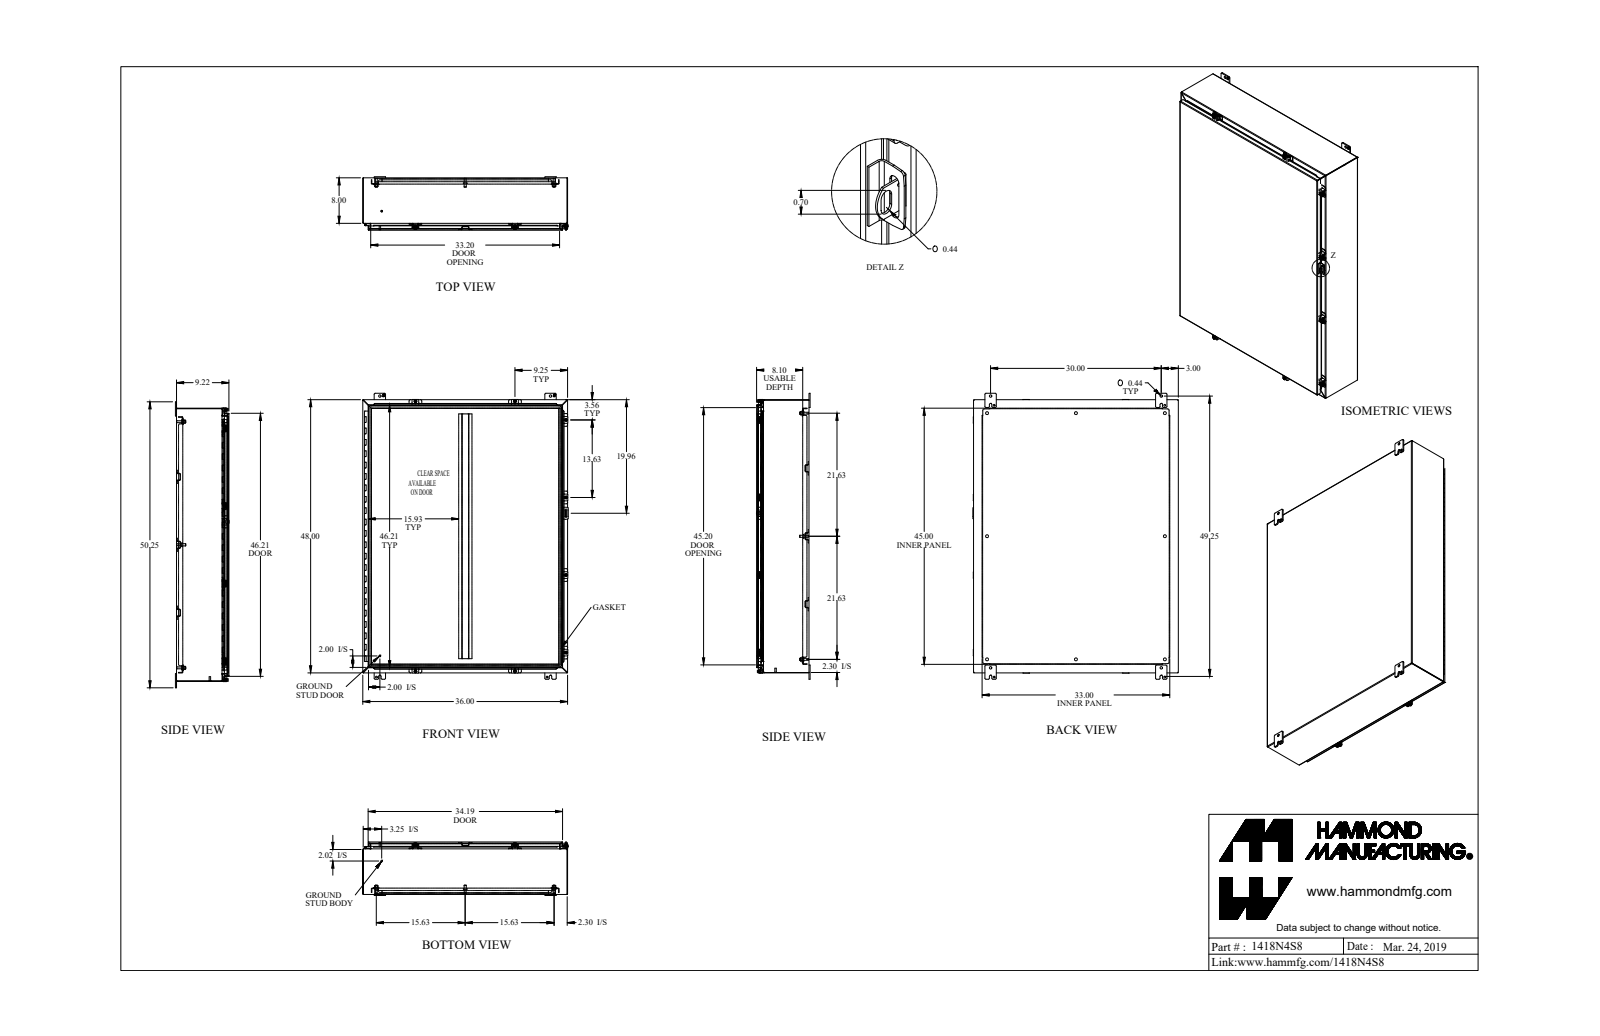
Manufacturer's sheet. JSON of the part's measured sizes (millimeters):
{"part_name": "1418N4S8_Default", "step_written_by": "SolidWorks 2019 (CONFIG_CONTROL_DESIGN)", "units": "millimeters", "bodies": {"solids": 67, "faces": 2413, "planar": 1405, "cylindrical": 876, "other": 132}, "overall_size": [1276.4, 917.6, 239.7], "volume_mm3": 9563000, "surface_area_mm2": 9792000, "round_holes": [[5.4, 8], [6.7, 8], [9.5, 8], [12.7, 8], [7.8, 4], [8, 4], [11.1, 4], [11.3, 4], [3.2, 1], [4.7, 1]], "round_bosses_or_shafts": [[16.5, 8], [12.7, 8], [9.9, 8], [9.5, 8], [8.4, 8], [6.2, 8], [25.4, 4], [7.1, 2]], "partial_cylinders_radius": [[6.4, 48], [1.2, 39], [3.6, 39], [4.8, 37], [0.9, 24], [2.7, 24], [2.9, 16], [3.6, 16]], "face_to_face_distances": [1.8, 232.2, 230.4, 234.1, 2.4, 206, 204.2, 26.2, 28, 208.4], "hole_center_spacings": [965.3, 182.8, 396.9, 621.5, 793.8, 1098.6, 1308.3, 549.3]}
